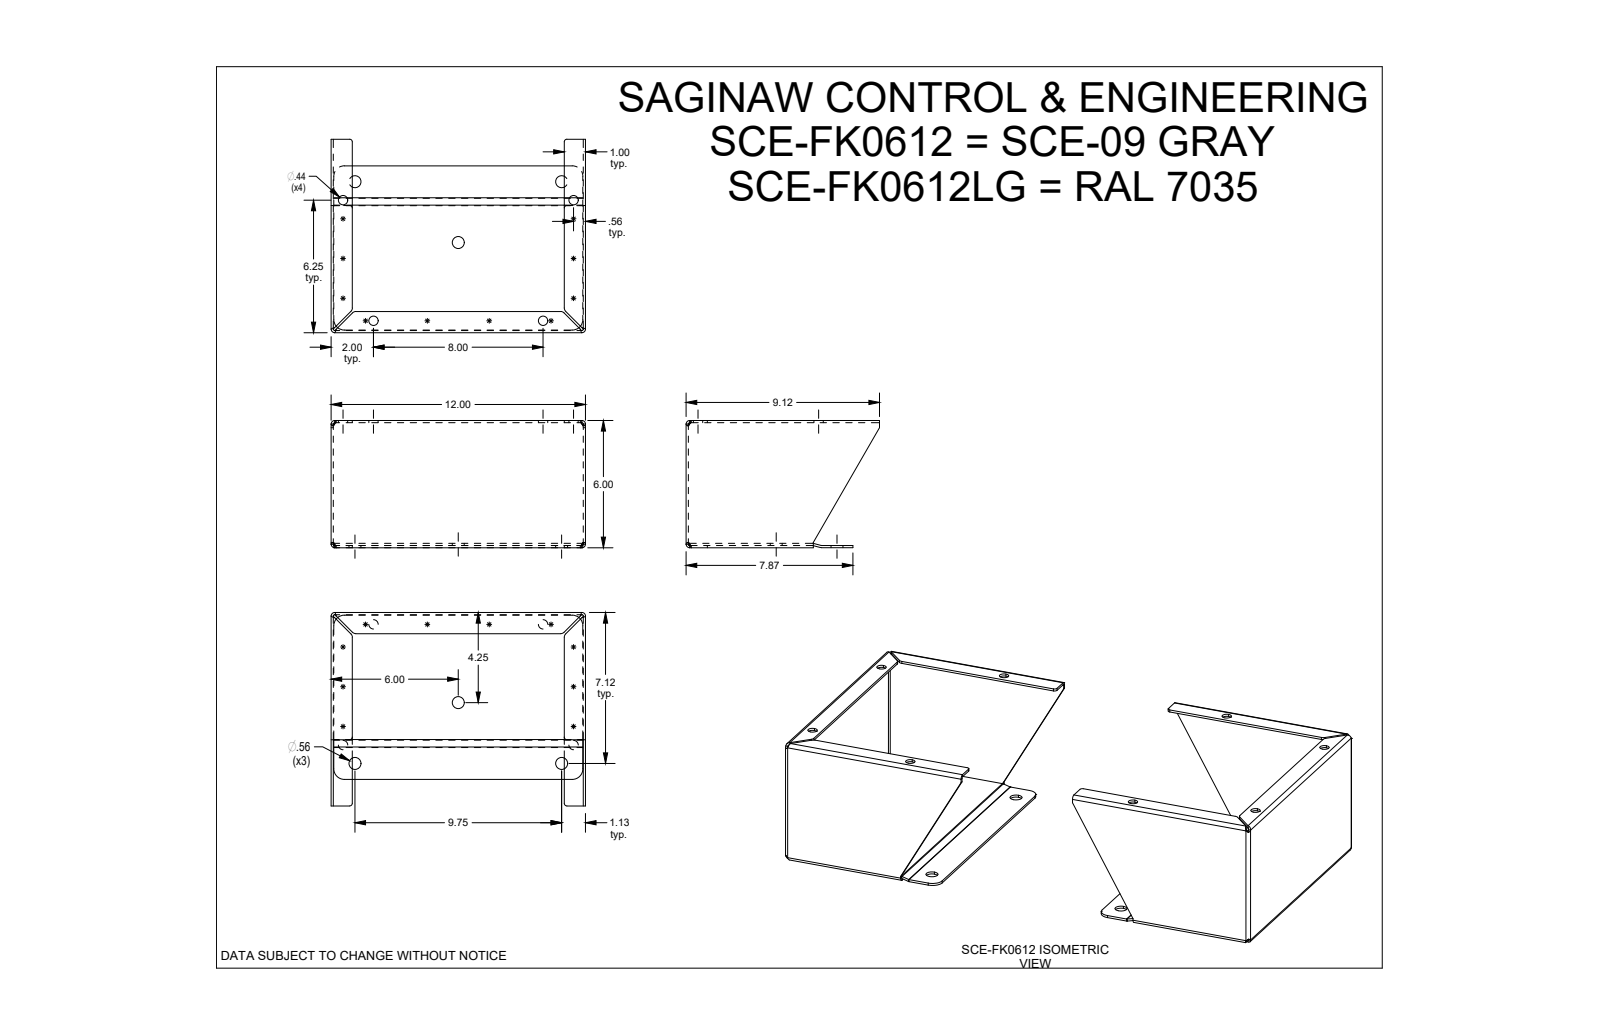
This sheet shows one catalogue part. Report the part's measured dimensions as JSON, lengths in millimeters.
{"part_name": "SCE-FK0612LG", "step_written_by": "SolidWorks 2019 (CONFIG_CONTROL_DESIGN)", "units": "millimeters", "bodies": {"solids": 4, "faces": 214, "planar": 96, "cylindrical": 86, "other": 32}, "overall_size": [609.6, 304.8, 152.4], "volume_mm3": 995500, "surface_area_mm2": 770300, "round_holes": [[11.1, 8], [14.3, 6]], "partial_cylinders_radius": [[4.2, 16], [1.6, 14], [3.2, 8], [5.6, 8], [12.7, 8], [1.6, 2]], "face_to_face_distances": [2.6, 302.2, 607, 147.1, 304.8, 299.5, 149.8, 2.6, 149.7, 609.6], "hole_center_spacings": [26.3, 138.2, 143.7, 147.1, 149, 168, 270.4, 279.9]}
